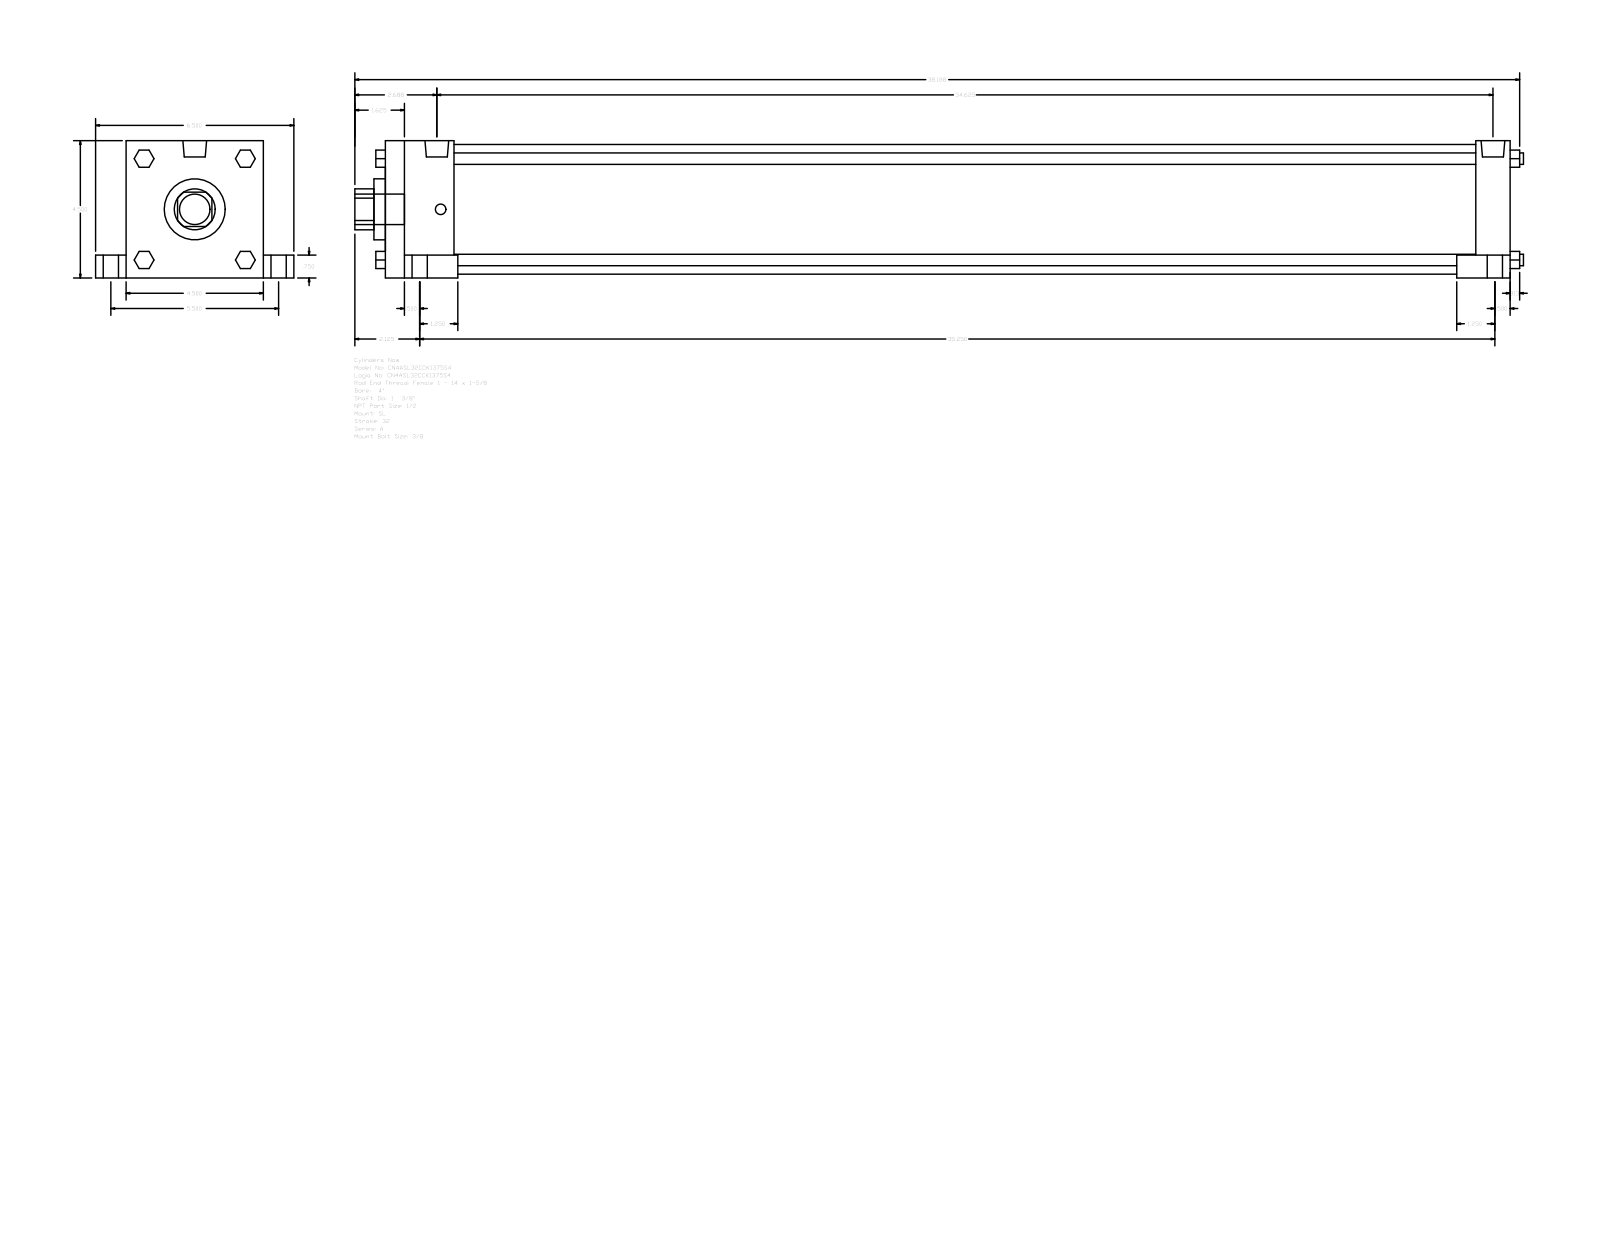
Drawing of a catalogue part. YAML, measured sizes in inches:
part_name: "A_SL__0400_1.375"
step_written_by: "GSSL Pune (CONFIG_CONTROL_DESIGN)"
units: inches
bodies: {solids: 0, faces: 150, planar: 114, cylindrical: 36, other: 0}
overall_size: [38.313, 6.5, 4.5]
round_holes:
  - {diameter: 1.375, count: 1}
  - {diameter: 2, count: 1}
  - {diameter: 4.25, count: 1}
round_bosses_or_shafts:
  - {diameter: 0.75, count: 4}
  - {diameter: 0.5, count: 4}
  - {diameter: 0.375, count: 4}
  - {diameter: 0.344, count: 4}
  - {diameter: 0.778, count: 2}
  - {diameter: 1, count: 1}
partial_cylinders:
  - {radius: 0.672, count: 1}
face_to_face_distances: [4.5, 36.875, 1.125, 1, 2.25, 34.625, 35.75, 33.5, 5.5, 0.75]
